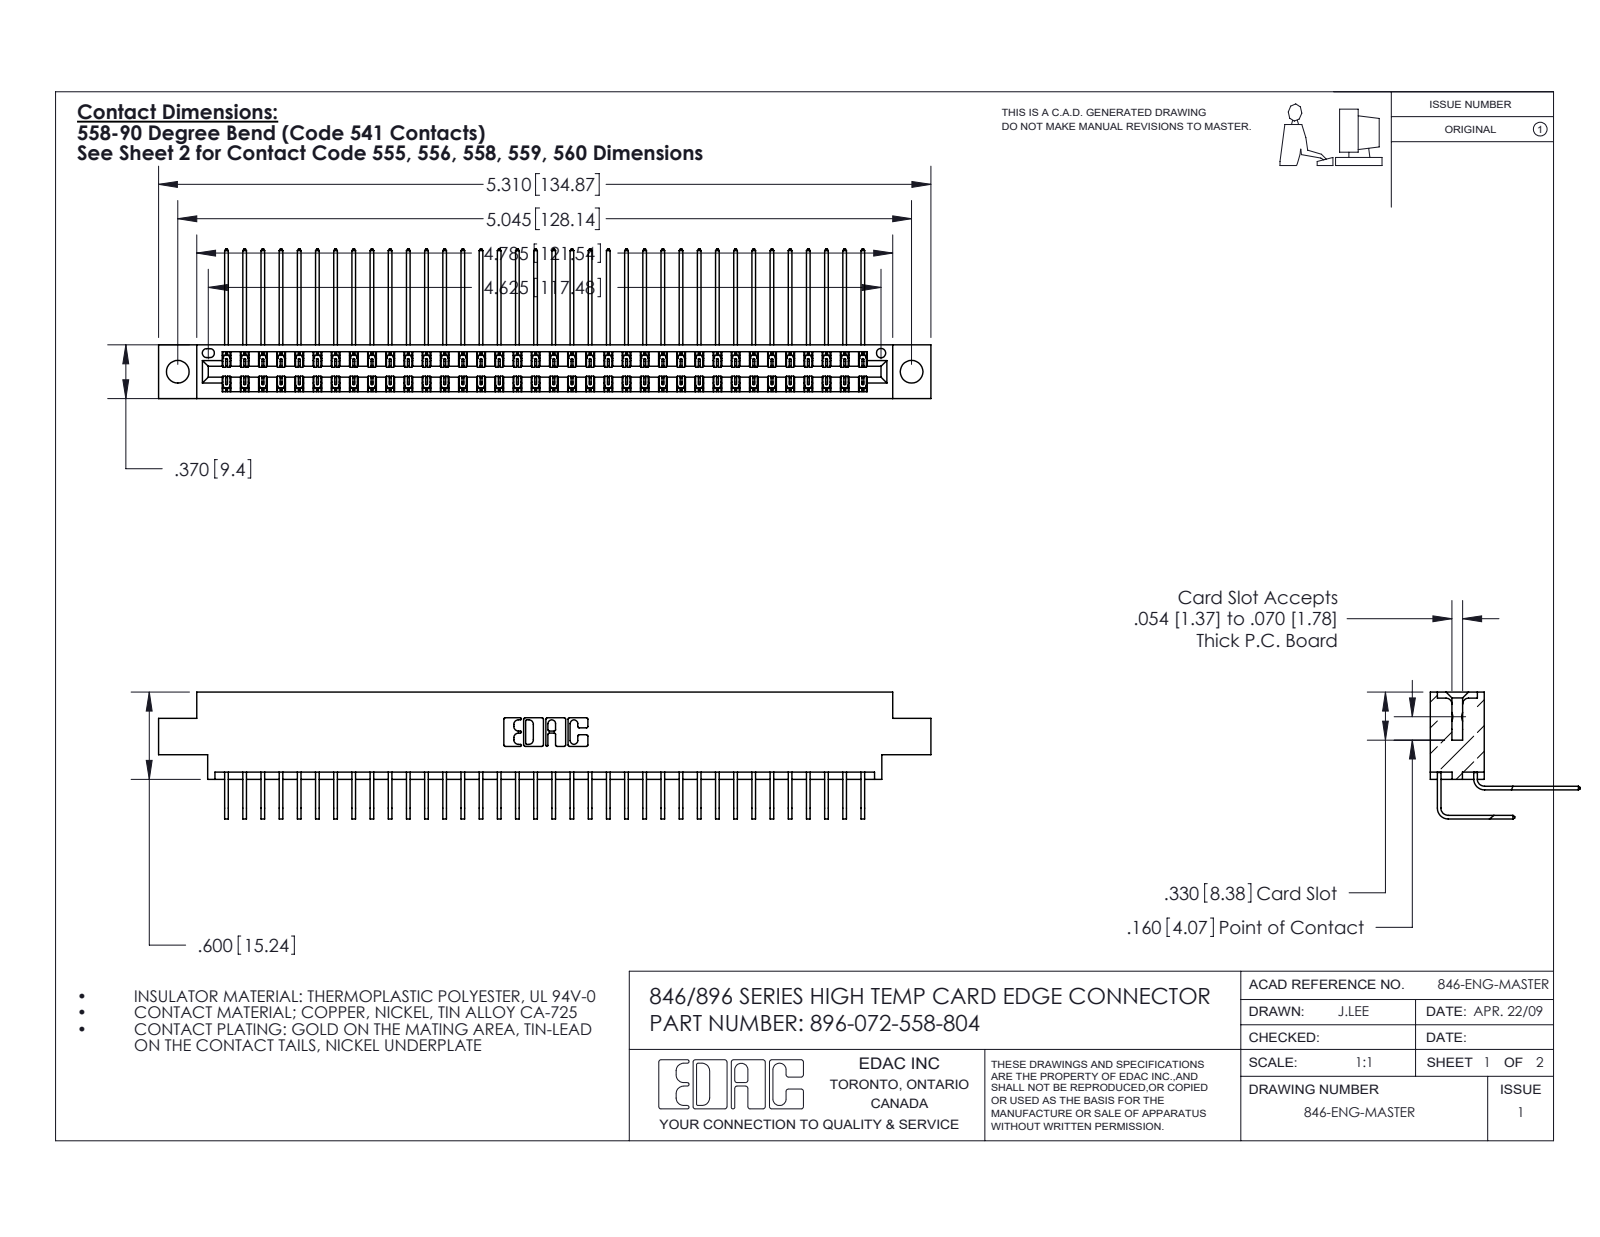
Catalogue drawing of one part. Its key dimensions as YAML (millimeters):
part_name: "345-292-001_558 Tail - 2; 346 Part_0.170 Offset - 0.156 Dia-TH; 345-292-001_558 559 Tail - 1; 396-072-558-804"
step_written_by: "SolidWorks 2016 (CONFIG_CONTROL_DESIGN)"
units: millimeters
bodies: {solids: 73, faces: 4014, planar: 2744, cylindrical: 1270, other: 0}
overall_size: [134.9, 26.2, 22.2]
volume: 13300
surface_area: 20140
round_holes:
  - {diameter: 4, count: 2}
  - {diameter: 1.6, count: 1}
partial_cylinders:
  - {radius: 0.2, count: 108}
  - {radius: 0.3, count: 22}
  - {radius: 0.2, count: 6}
  - {radius: 0.8, count: 6}
  - {radius: 0.7, count: 3}
  - {radius: 0.4, count: 2}
  - {radius: 0.6, count: 2}
  - {radius: 0.6, count: 2}
face_to_face_distances: [8.2, 1.2, 0.6, 9.4, 6.4, 7.6, 1.8, 7, 3.8, 5.6]
hole_center_spacings: [6.2, 122.8, 128.1]
